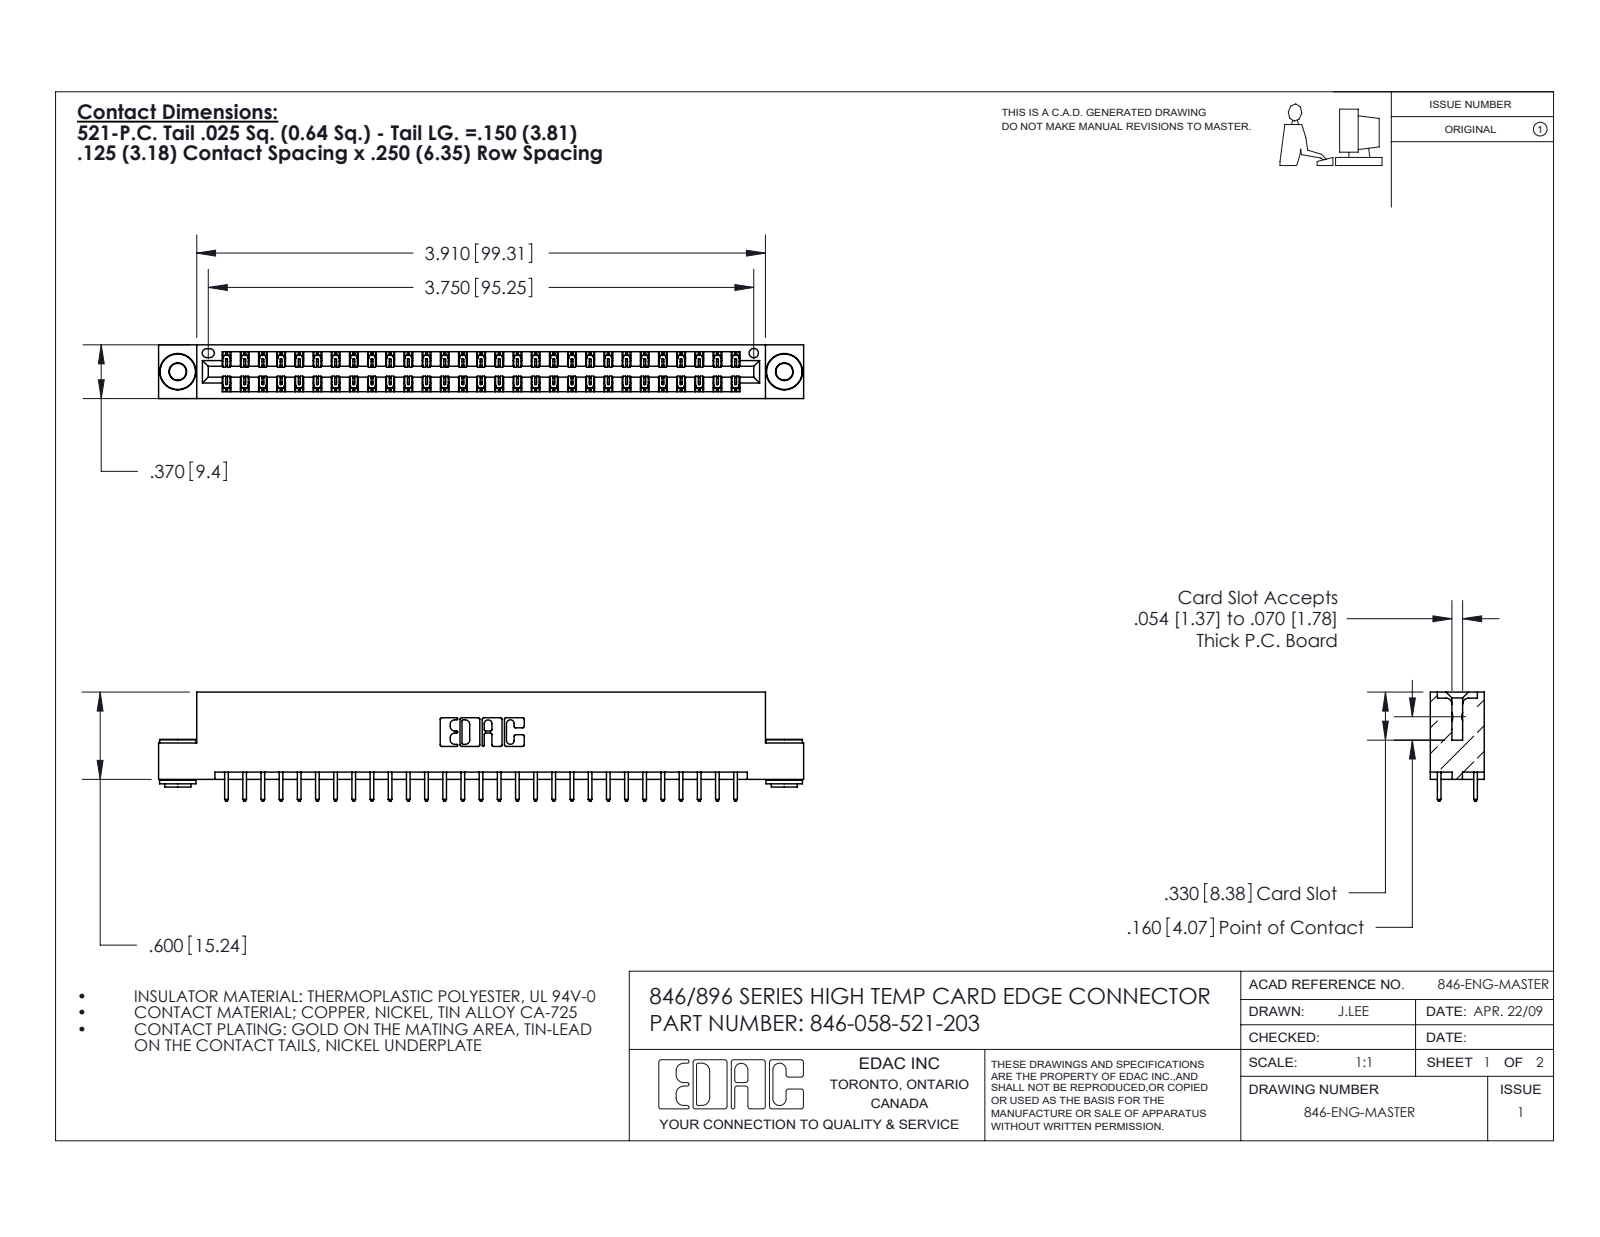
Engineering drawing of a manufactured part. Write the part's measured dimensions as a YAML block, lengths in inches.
part_name: "346 Part_Flush Mounting Lugs - 0.156 Dia-TH; 346-058-521-203; 345-250-002_345-250-002-102; 345-292-001_345-293-121"
step_written_by: "SolidWorks 2016 (CONFIG_CONTROL_DESIGN)"
units: inches
bodies: {solids: 61, faces: 3176, planar: 2116, cylindrical: 1052, other: 8}
overall_size: [4.435, 0.75, 0.37]
volume: 0.664
surface_area: 22.95
round_holes:
  - {diameter: 0.116, count: 2}
  - {diameter: 0.156, count: 2}
  - {diameter: 0.064, count: 1}
round_bosses_or_shafts:
  - {diameter: 0.25, count: 2}
  - {diameter: 0.18, count: 2}
  - {diameter: 0.136, count: 2}
partial_cylinders:
  - {radius: 0.006, count: 87}
  - {radius: 0.01, count: 58}
  - {radius: 0.01, count: 22}
  - {radius: 0.007, count: 6}
  - {radius: 0.031, count: 6}
  - {radius: 0.026, count: 3}
  - {radius: 0.014, count: 2}
  - {radius: 0.022, count: 2}
face_to_face_distances: [0.048, 0.322, 0.25, 0.37, 0.025, 0.072, 0.298, 0.275, 0.148, 0.222]
hole_center_spacings: [0.246, 3.962, 4.17]
